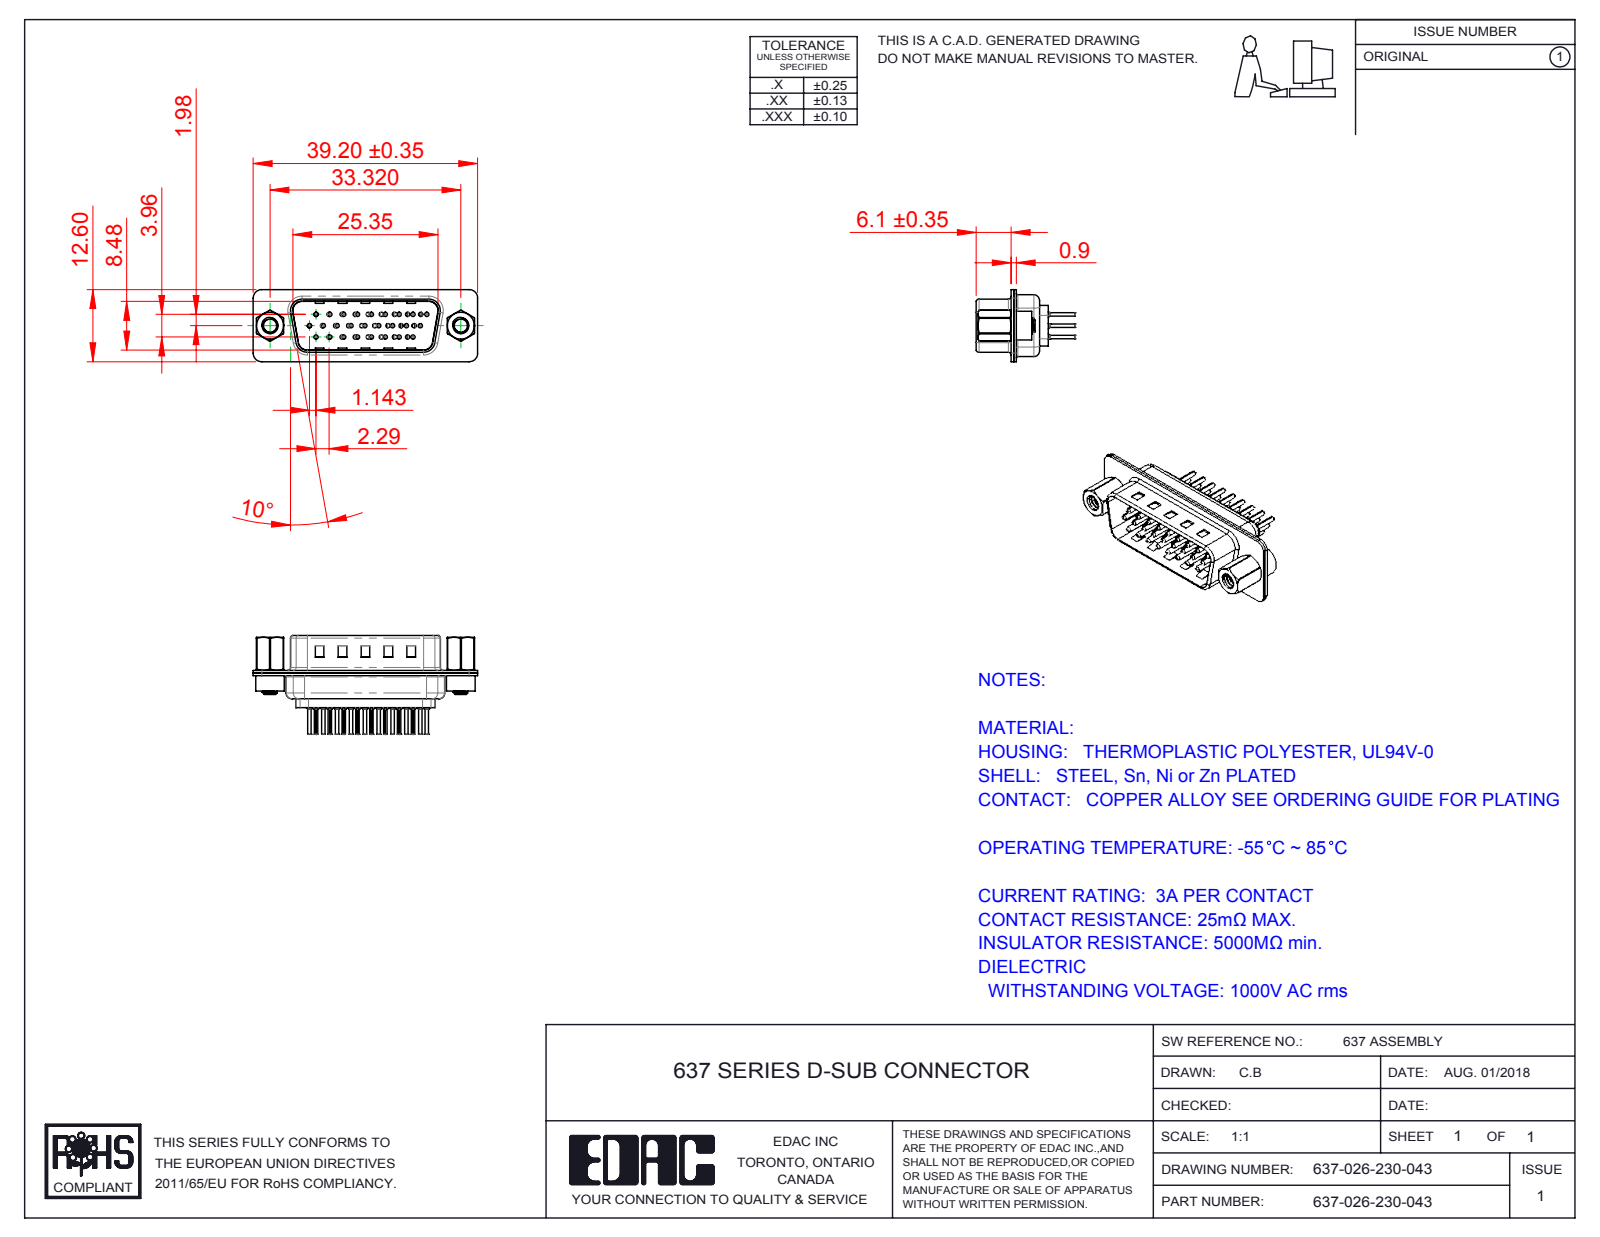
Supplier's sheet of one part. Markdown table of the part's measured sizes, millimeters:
| quantity | value |
| --- | --- |
| part name | 637 Shell Rear_26 Contacts; 637 4-40 Threaded Rivet; 637 4-40 Hex Standoff; 637 Housing_26 Contacts (+5 more) |
| STEP written by | SolidWorks 2016 (CONFIG_CONTROL_DESIGN) |
| units | millimeters |
| bodies | 33 solids, 3066 faces (785 planar, 1167 cylindrical, 1114 other) |
| overall size | 39.2 × 17.25 × 12.6 |
| volume | 2 041 mm³ |
| surface area | 7 176 mm² |
| round holes (diameter × count) | 1.6 × 49, 0.2 × 26, 0.35 × 26, 1.1 × 26, 0.75 × 23, 2 × 23, 2.26 × 2, 2.29 × 2, 4 × 2, 4.8 × 2 |
| round bosses / shafts (diameter × count) | 2 × 26, 1.5 × 26, 0.75 × 26, 0.6 × 26, 5 × 2, 4.9 × 2, 2.79 × 2 |
| partial cylindrical surfaces (radius × count) | 0.1 × 52, 1.5 × 16, 2 × 12, 0.5 × 8, 0.25 × 4, 0.55 × 4, 0.7 × 4, 0.95 × 4 |
| main face-to-face distances | 0.45, 0.4, 0.9, 8.48, 0.7, 8.88, 0.31, 1.05, 4.55, 1.16 |
| hole center spacings | 3.96, 2.28, 4.57, 6.05, 2.29, 8.24, 6.86, 10.48 |
